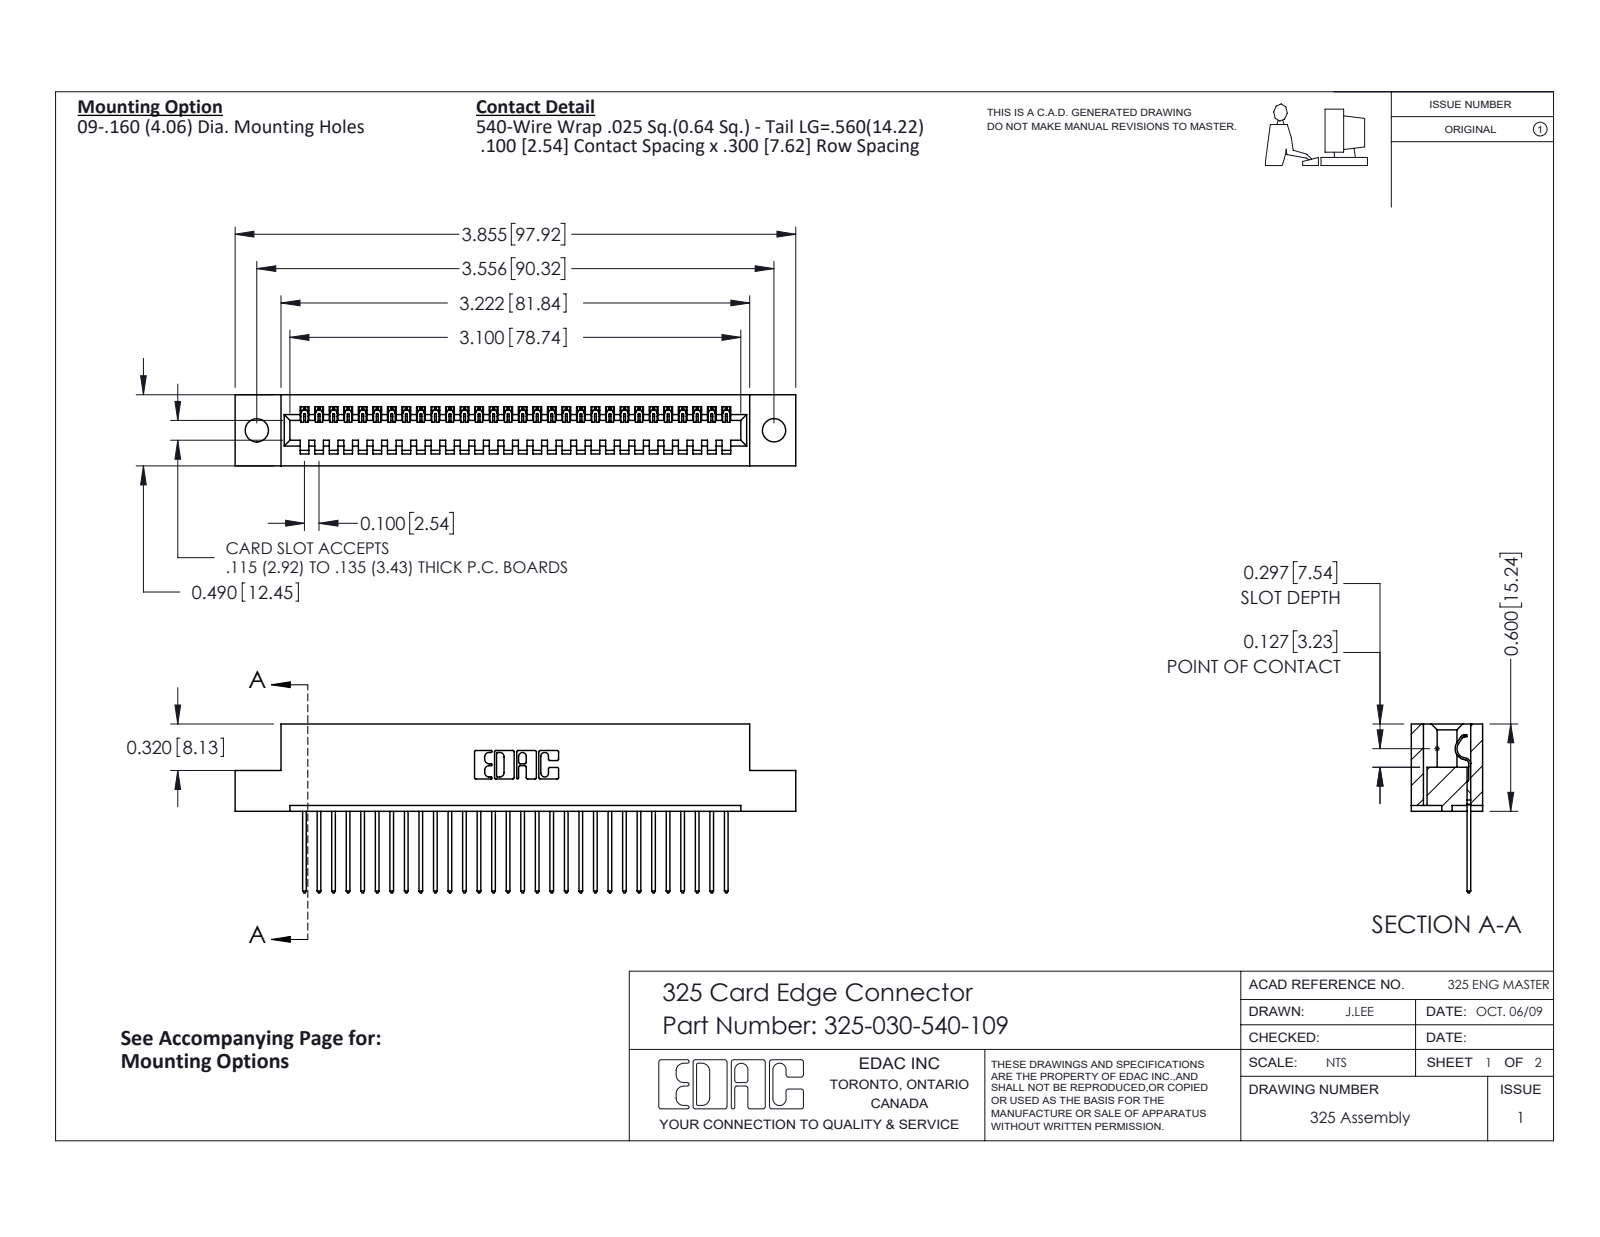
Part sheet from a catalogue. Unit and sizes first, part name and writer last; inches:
Units: inches
Overall size (bounding box): 3.855 × 1.16 × 0.49
Round holes (diameter × count): ⌀0.16 ×2
Partial cylindrical surfaces — rounded edges, fillets, slot ends (radius × count): R0.006 ×60, R0.01 ×60, R0.01 ×22, R0.007 ×6, R0.031 ×6, R0.026 ×3, R0.014 ×1, R0.022 ×1
Main face-to-face distances: 0.083, 0.407, 0.49, 0.3, 0.107, 0.383, 0.025, 0.325, 0.04, 0.56
Hole centre spacings: 3.556
Volume: 0.741 in³ · Surface area: 20.56 in²
Bodies: 31 solids, 1854 faces (1330 planar, 524 cylindrical, 0 other)
Part name (STEP PRODUCT): 325 Part_.160 TH; 325-030-540-109; 325-292-001_325-293-140
STEP written by: SolidWorks 2016 (CONFIG_CONTROL_DESIGN)
